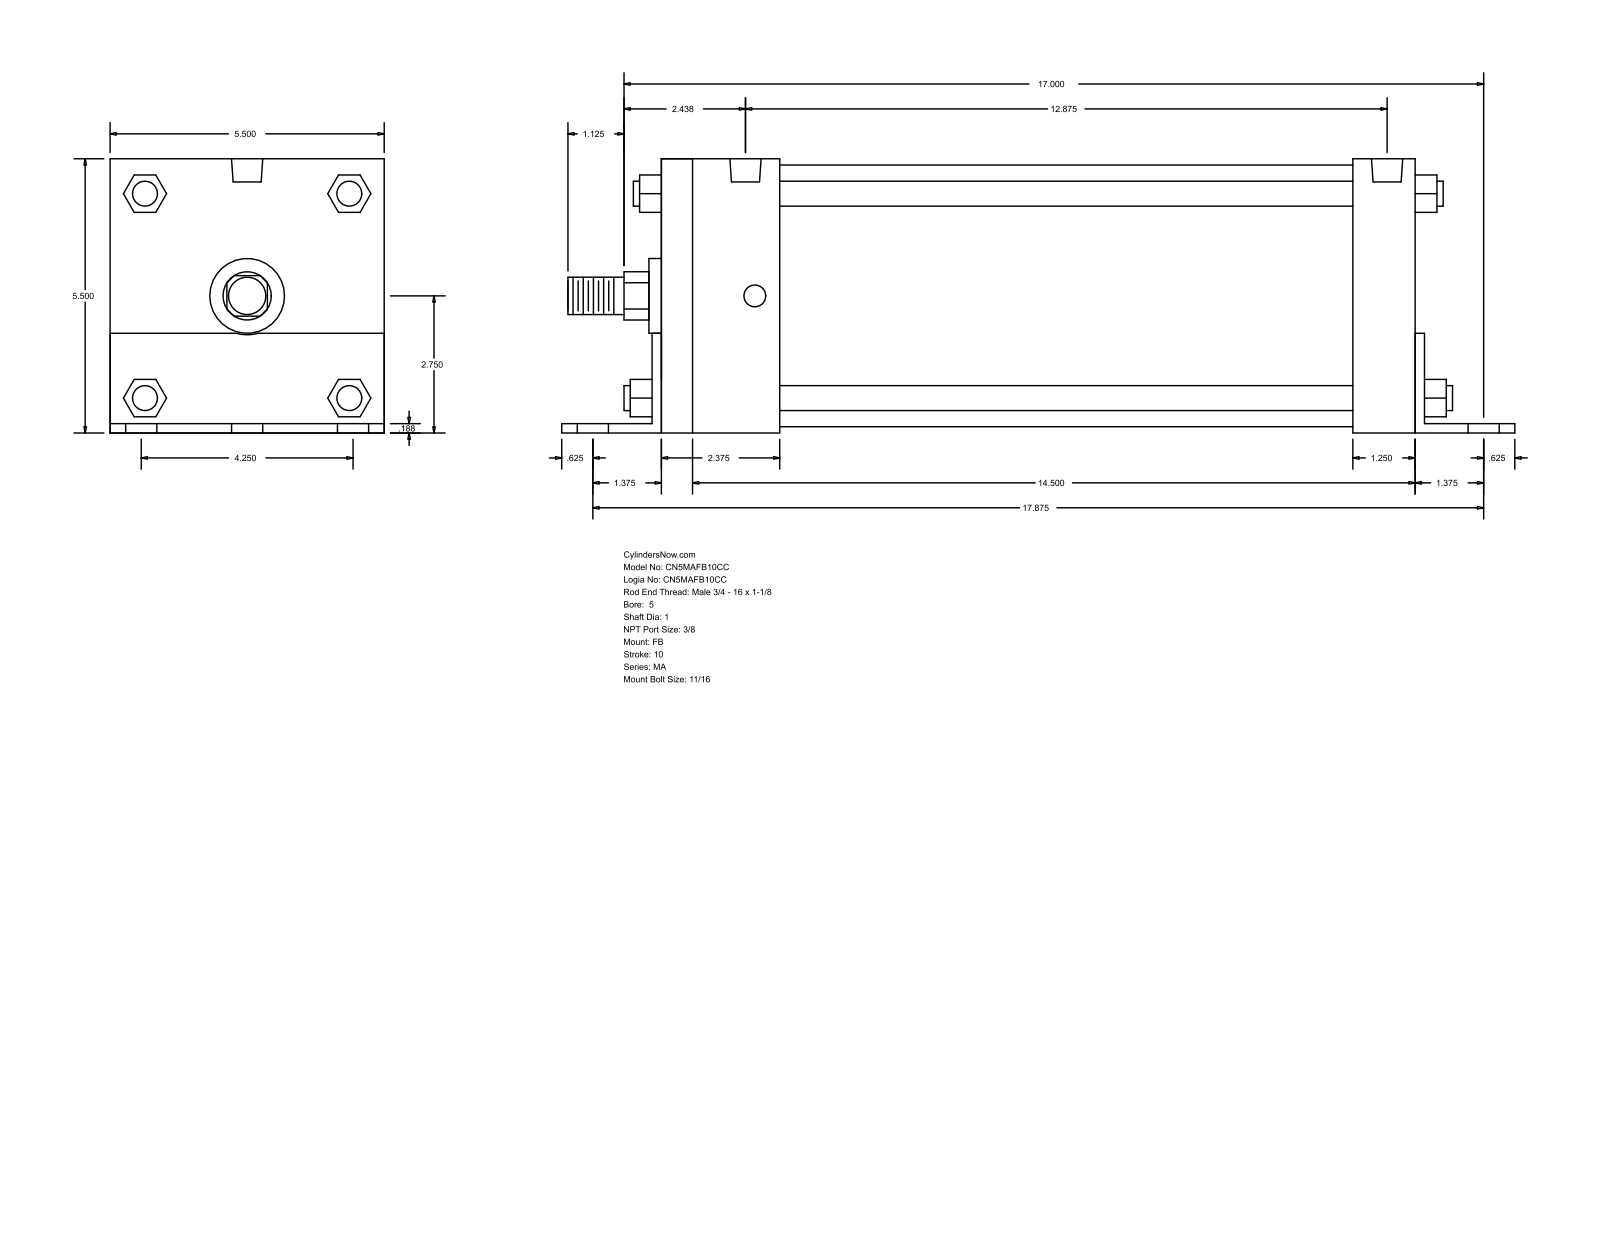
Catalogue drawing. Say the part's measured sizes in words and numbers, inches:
The part is named "MA_FB__0500_1". Its 3-D file was written by "GSSL Pune (CONFIG_CONTROL_DESIGN)". It is 0 solids with 140 faces: 105 planar, 35 cylindrical and 0 other. Overall it measures 19.125 by 5.502 by 5.5 inches. Round holes: 6 of diameter 0.687, 4 of diameter 0.437, 2 of diameter 0.627. Round bosses or shafts: 4 of diameter 0.5, 1 of diameter 5.25, 1 of diameter 1.5, 1 of diameter 1, 1 of diameter 0.75. Partial cylindrical surfaces (rounded edges, fillets, slot ends): 1 of radius 0.484, 1 of radius 0.78. The main face-to-face distances are 5.5, 0.187, 5.502, 15.313, 0.185, 5.315, 15.125, 15.5, 1.437, 1.25. The hole center spacings are 2.125, 18.001, 17.875, 0.187, 2.876, 3.005, 3.728, 3.883.
